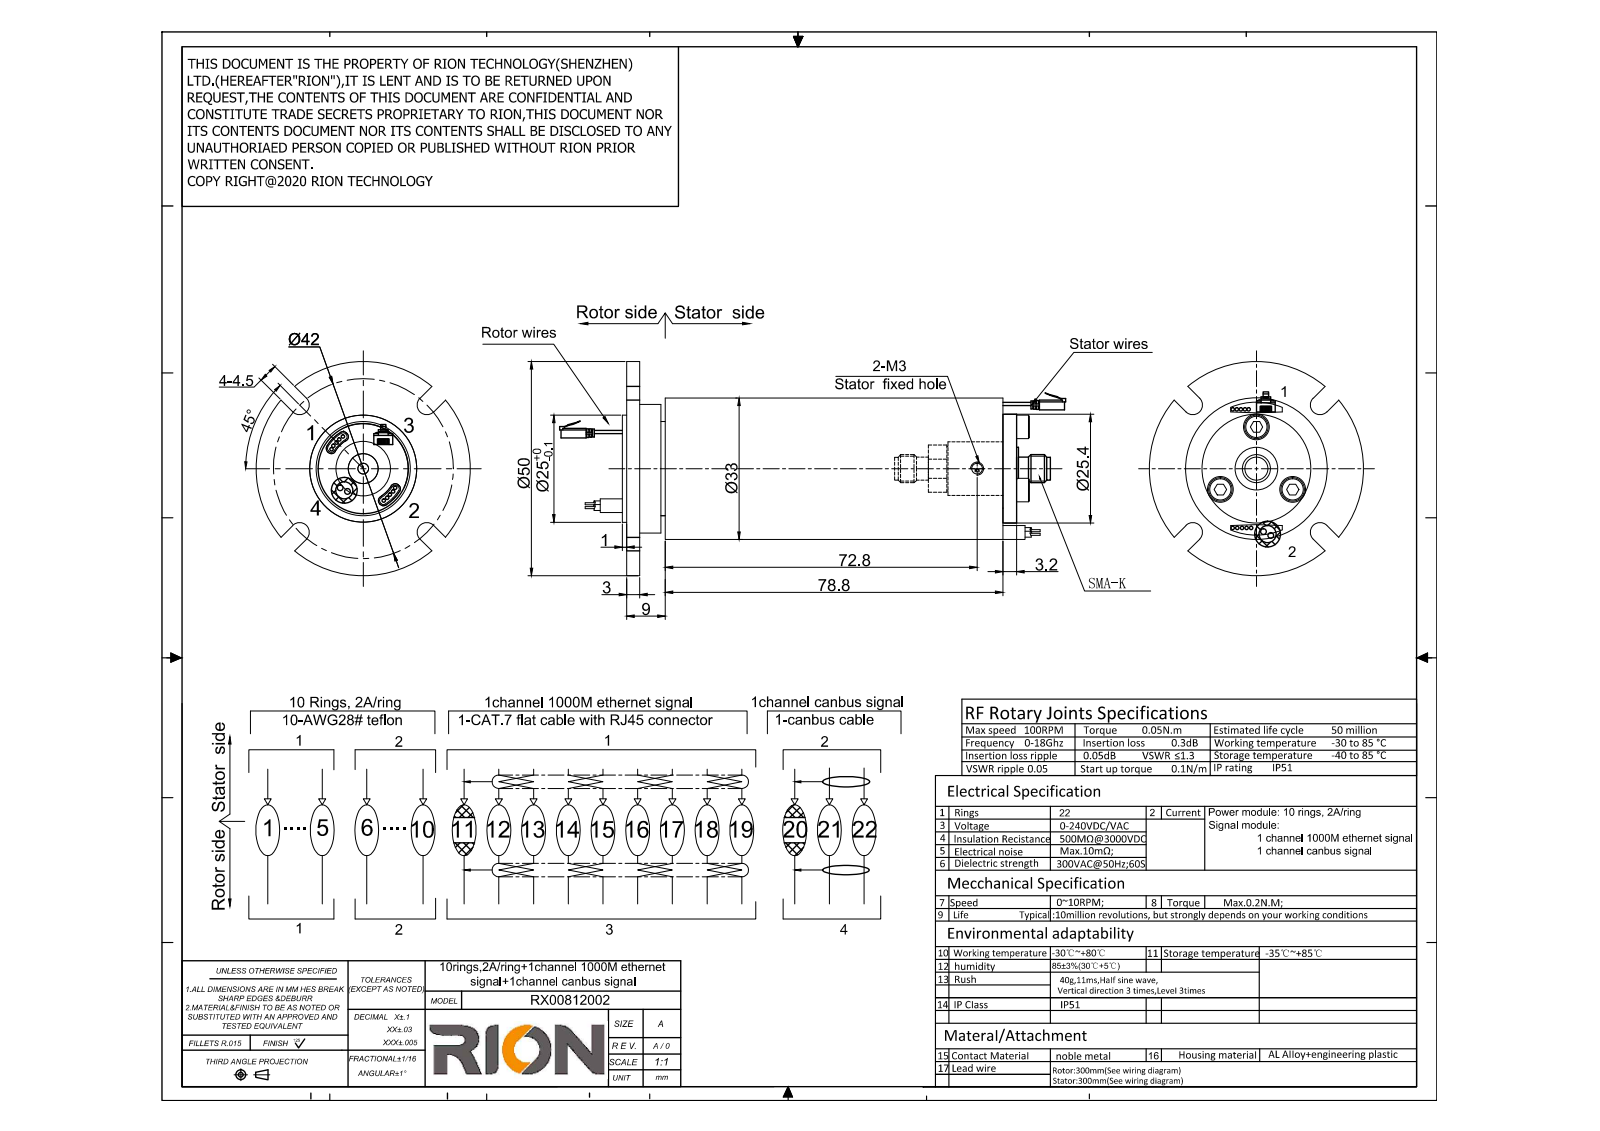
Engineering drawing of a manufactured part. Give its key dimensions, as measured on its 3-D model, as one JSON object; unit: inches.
{"part_name": "RX00812002--RHF107-P1002-1E-1C", "step_written_by": "SolidWorks 2014 (AUTOMOTIVE_DESIGN)", "units": "inches", "bodies": {"solids": 1, "faces": 221, "planar": 91, "cylindrical": 116, "other": 14}, "overall_size": [4.181, 1.969, 1.969], "volume_in3": 4.787, "surface_area_in2": 26.17, "round_holes": [[0.098, 1], [0.5, 1], [0.787, 1], [1.22, 1]], "round_bosses_or_shafts": [[0.031, 20], [0.217, 4], [1.969, 1], [1.299, 1], [1.217, 1], [1.181, 1], [1, 1], [0.984, 1]], "partial_cylinders_radius": [[0.05, 8], [0.089, 4], [0.294, 1], [0.606, 1]], "face_to_face_distances": [0.118, 0.354, 0.039, 0.236, 3.583, 3.465, 3.228, 0.126, 3.457, 0.315]}
